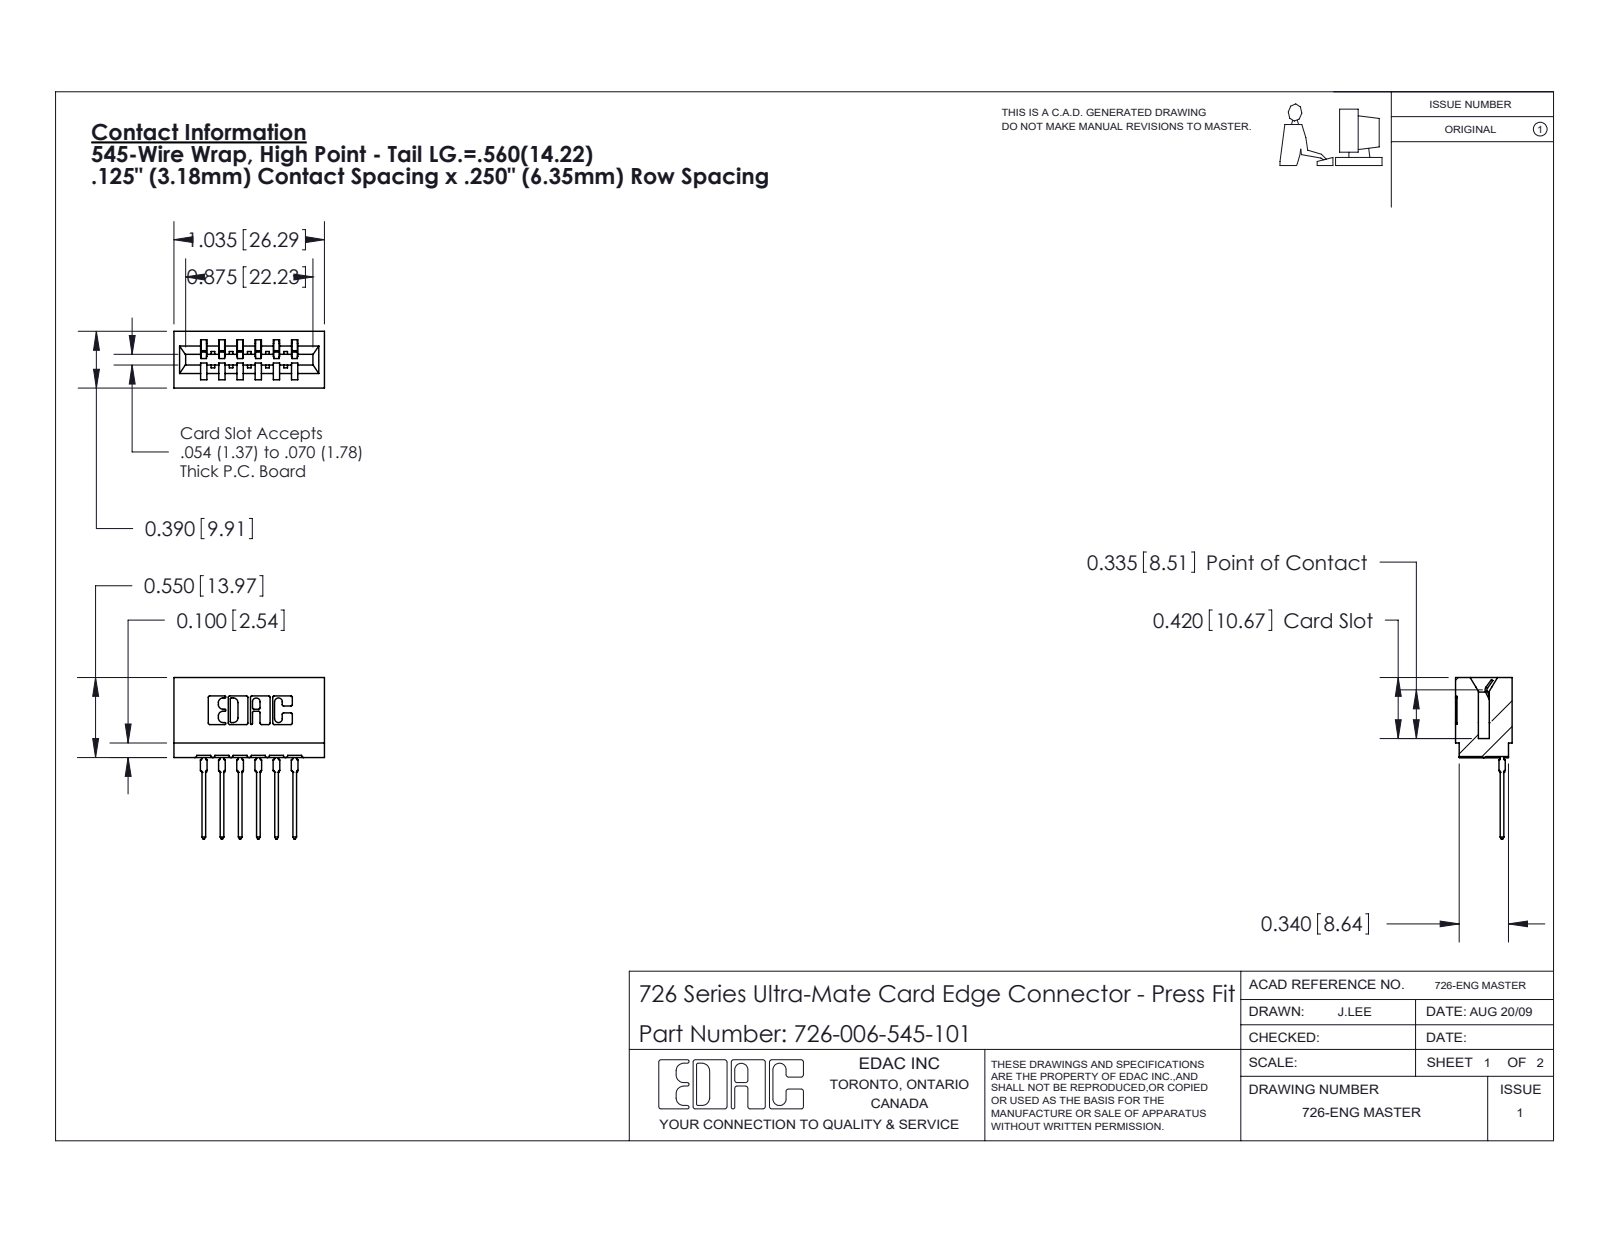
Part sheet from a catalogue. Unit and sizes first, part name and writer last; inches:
Units: inches
Overall size (bounding box): 1.109 × 1.035 × 0.39
Partial cylindrical surfaces — rounded edges, fillets, slot ends (radius × count): R0.01 ×22, R0.021 ×12, R0.015 ×7, R0.007 ×6, R0.031 ×6, R0.005 ×4, R0.011 ×4, R0.026 ×3
Main face-to-face distances: 0.25, 0.125, 0.042, 0.057, 0.333, 0.375, 0.125, 0.292, 0.5, 0.208
Volume: 0.157 in³ · Surface area: 5.388 in²
Bodies: 7 solids, 745 faces (433 planar, 156 cylindrical, 156 other)
Part name (STEP PRODUCT): 726-006-545-101; 726 Part_.515 Slot Depth - 01; 746-292-001_545
STEP written by: SolidWorks 2020 (CONFIG_CONTROL_DESIGN)
